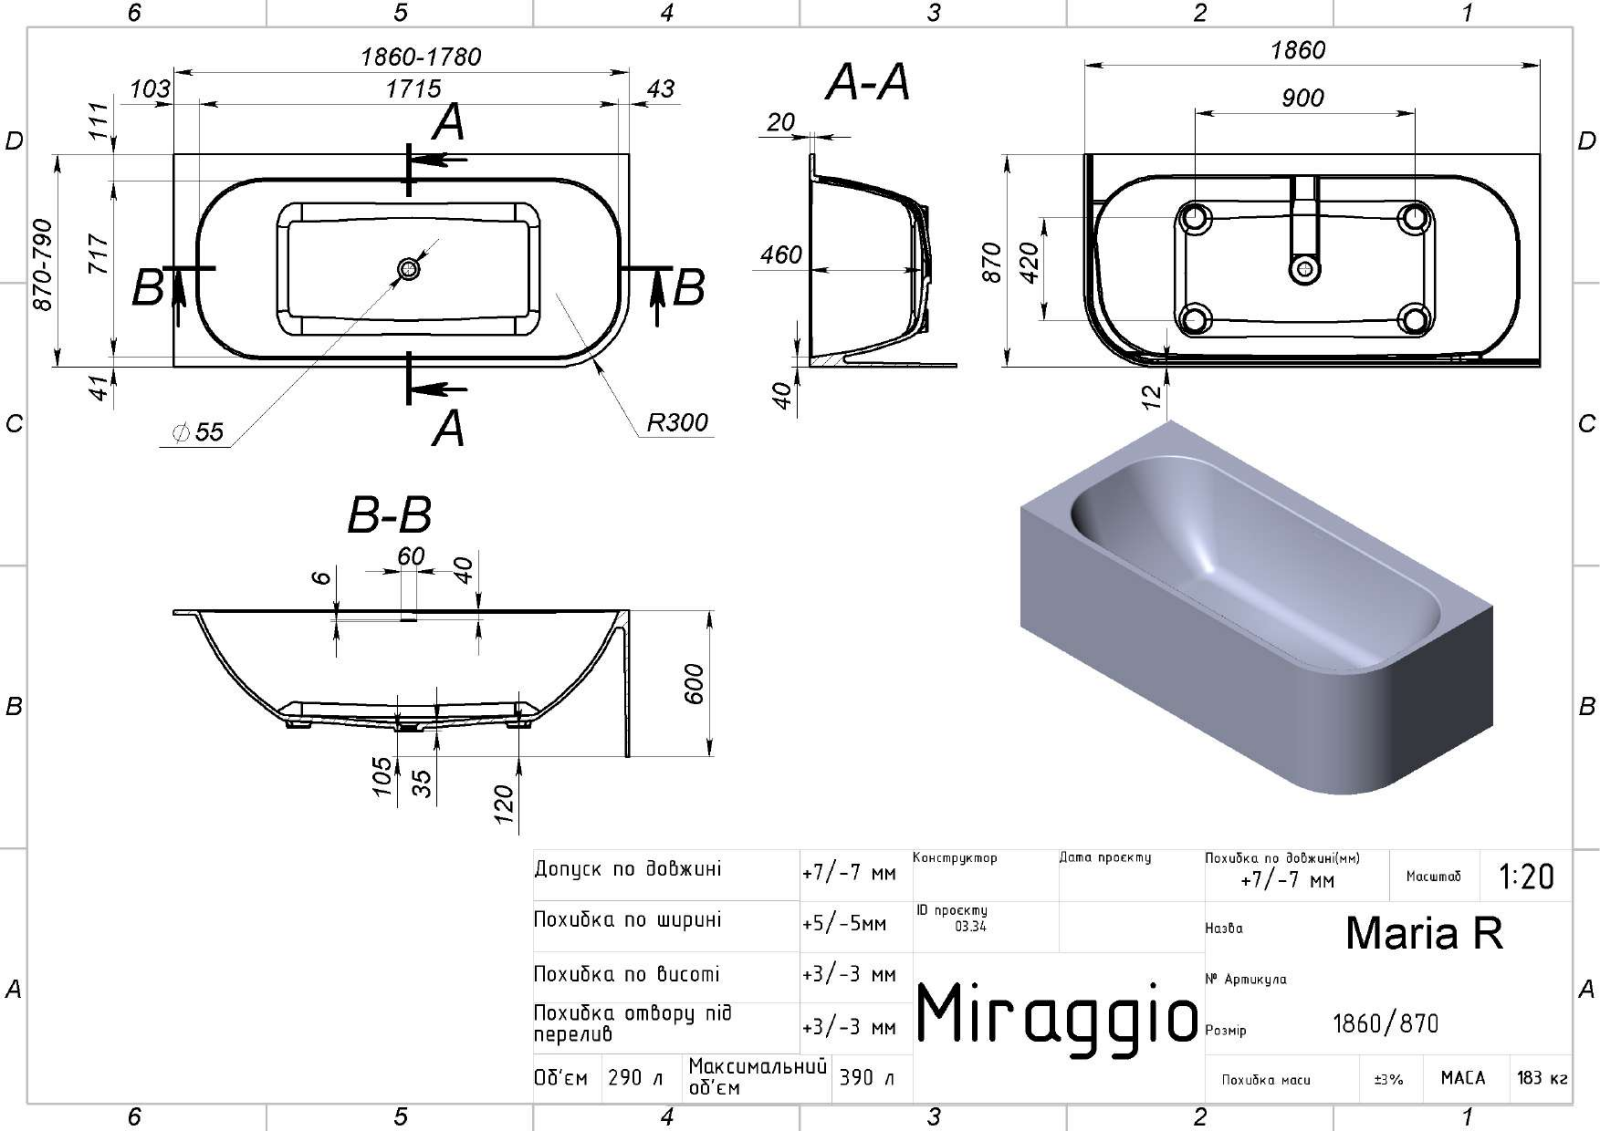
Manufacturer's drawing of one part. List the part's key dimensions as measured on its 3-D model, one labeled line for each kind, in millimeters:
Part name (STEP PRODUCT): Maria R
STEP written by: SolidWorks 2020 (AUTOMOTIVE_DESIGN)
Units: millimetres
Bodies: 1 solid, 164 faces (31 planar, 22 cylindrical, 111 other)
Overall size (bounding box): 1860 × 870 × 600
Volume: 77 860 000 mm³ · Surface area: 8 276 000 mm²
Round holes (diameter × count): ⌀55 ×1
Partial cylindrical surfaces — rounded edges, fillets, slot ends (radius × count): R10 ×5, R50 ×3, R3 ×2, R90 ×1, R97 ×1, R104 ×1, R300 ×1, R2188.55 ×1
Main face-to-face distances: 20, 870, 460, 120, 580, 600, 1860, 480, 140, 340
